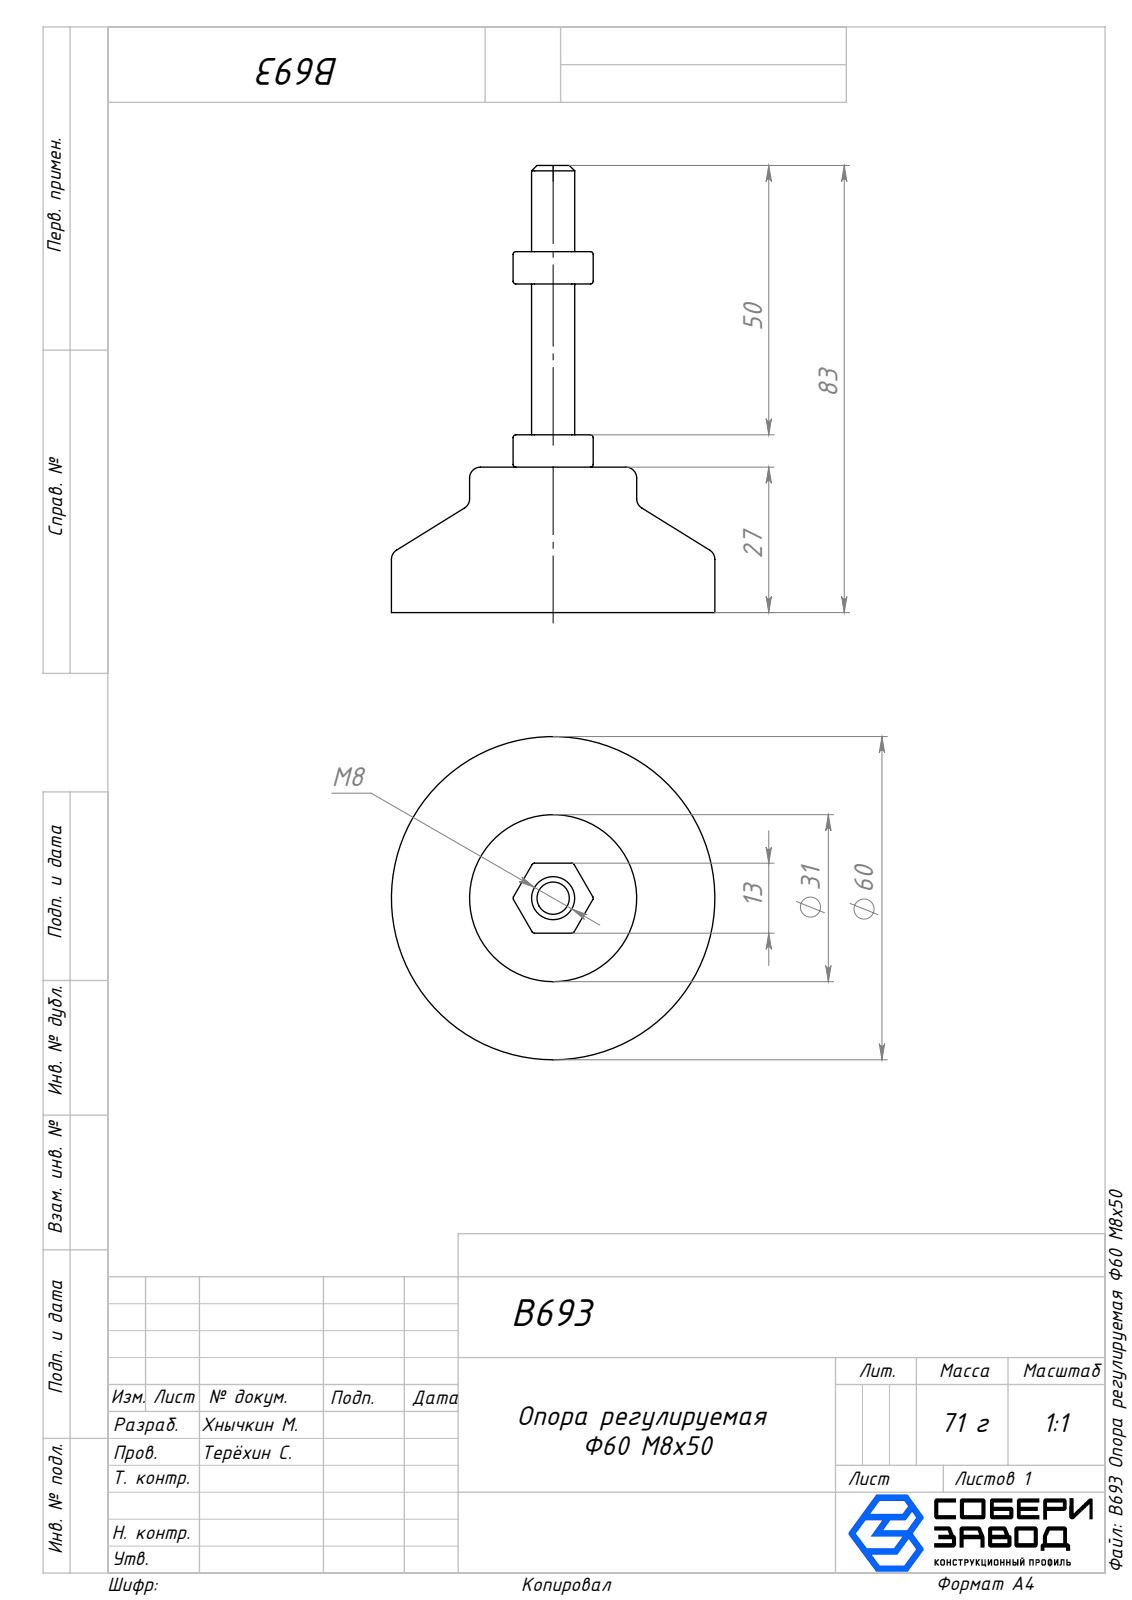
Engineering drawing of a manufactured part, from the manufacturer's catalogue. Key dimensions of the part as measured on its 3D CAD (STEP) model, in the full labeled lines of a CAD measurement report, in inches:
Part name (STEP PRODUCT): B693 Опора регулируемая Ф60 М8х50; Мал.гайка_00; Вал_00; Опора_00 (+1 more)
STEP written by: SolidWorks 2025 (AUTOMOTIVE_DESIGN)
Units: inches
Bodies: 4 solids, 157 faces (29 planar, 70 cylindrical, 58 other)
Overall size (bounding box): 3.268 × 2.362 × 2.362
Volume: 2.865 in³ · Surface area: 20.41 in²
Round holes (diameter × count): ⌀0.157 ×1, ⌀0.236 ×1, ⌀1.299 ×1
Round bosses / shafts (diameter × count): ⌀2.362 ×1, ⌀1.22 ×1, ⌀0.315 ×1, ⌀0.197 ×1
Partial cylindrical surfaces — rounded edges, fillets, slot ends (radius × count): R0.02 ×42
Main face-to-face distances: 0.433, 1.063, 0.63, 0.512, 0.236, 2.402, 1.339, 1.969, 2.205, 0.197
